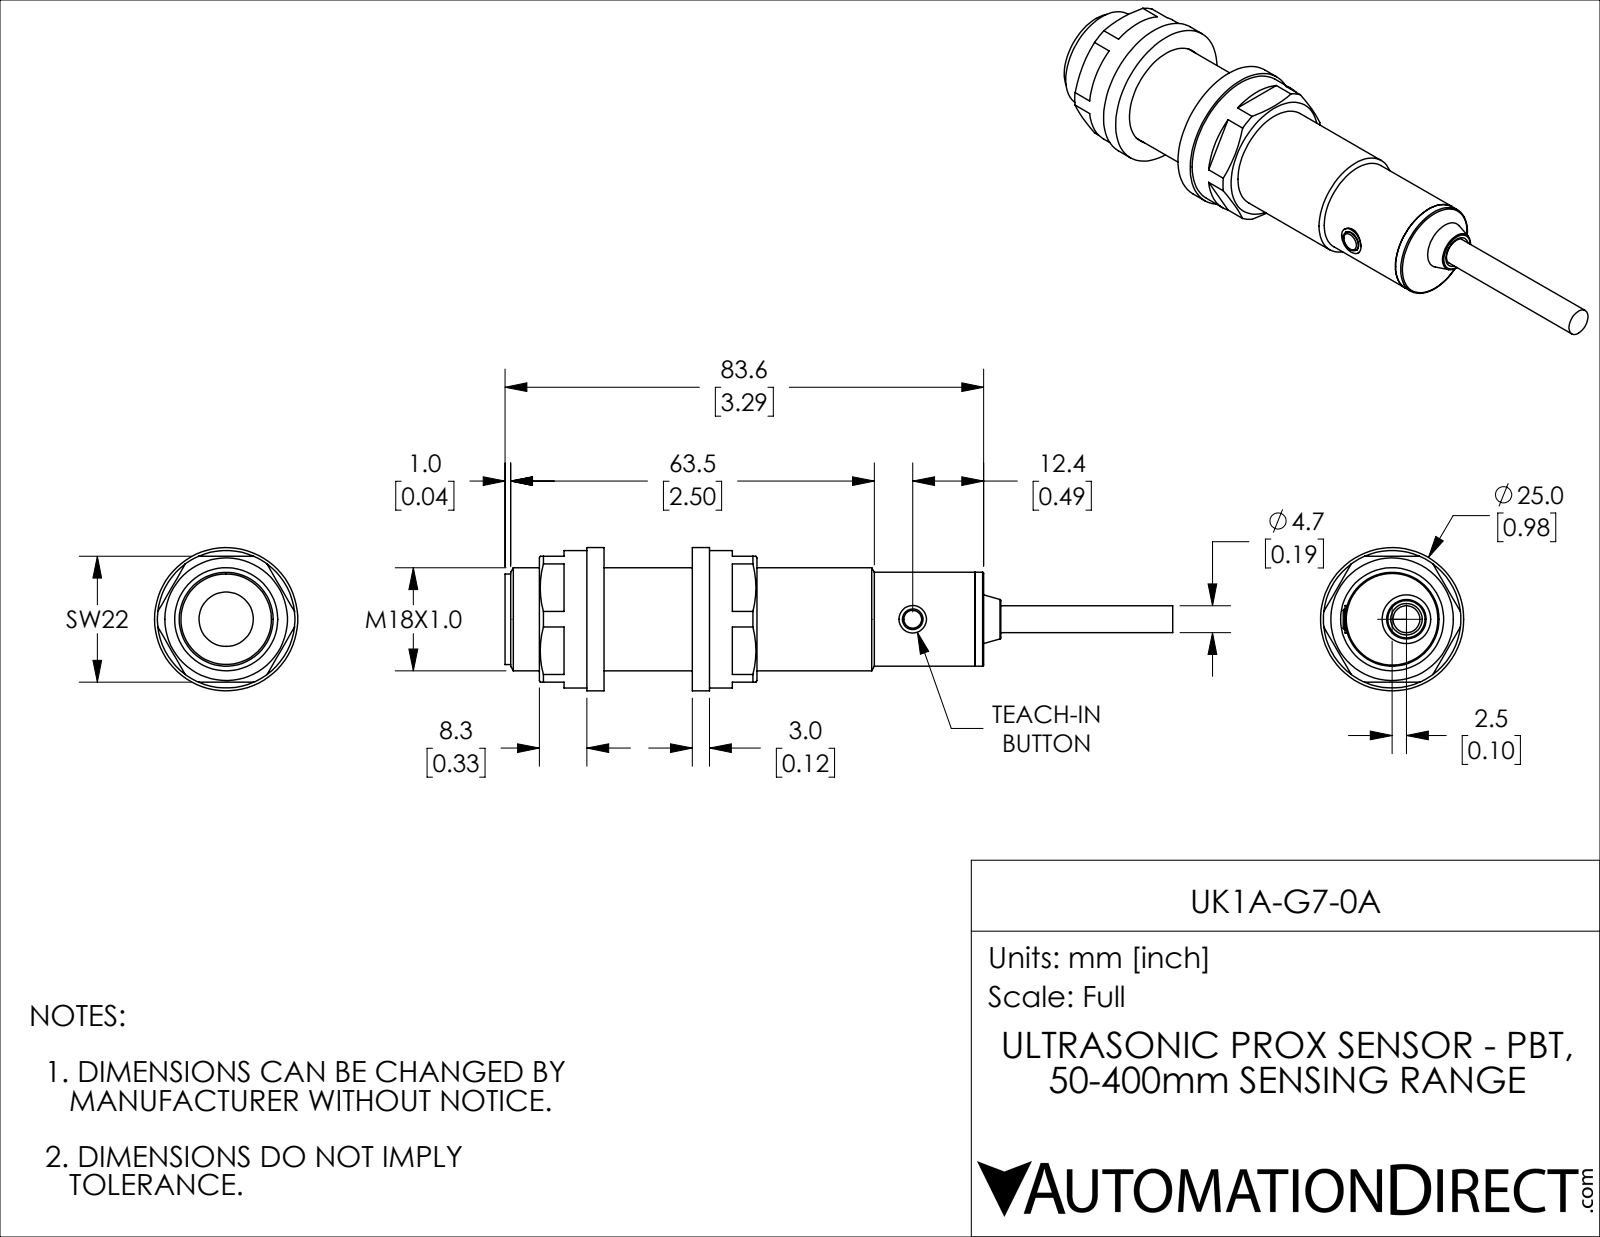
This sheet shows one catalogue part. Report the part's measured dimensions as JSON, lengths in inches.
{"part_name": "UK1A-G7-0A", "step_written_by": "SolidWorks 2018 (AUTOMOTIVE_DESIGN)", "units": "inches", "bodies": {"solids": 10, "faces": 107, "planar": 49, "cylindrical": 40, "other": 18}, "overall_size": [4.591, 0.984, 0.984], "volume_in3": 1.539, "surface_area_in2": 17.7, "round_holes": [[0.185, 2], [0.142, 1], [0.374, 1], [0.709, 1], [0.717, 1]], "round_bosses_or_shafts": [[0.984, 1], [0.945, 1], [0.646, 1], [0.622, 1], [0.213, 1], [0.189, 1]], "face_to_face_distances": [0.118, 0.724, 0.843, 2.669, 1.827, 0.524, 1.366, 3.193, 0.642, 2.551], "hole_center_spacings": [0.098]}
